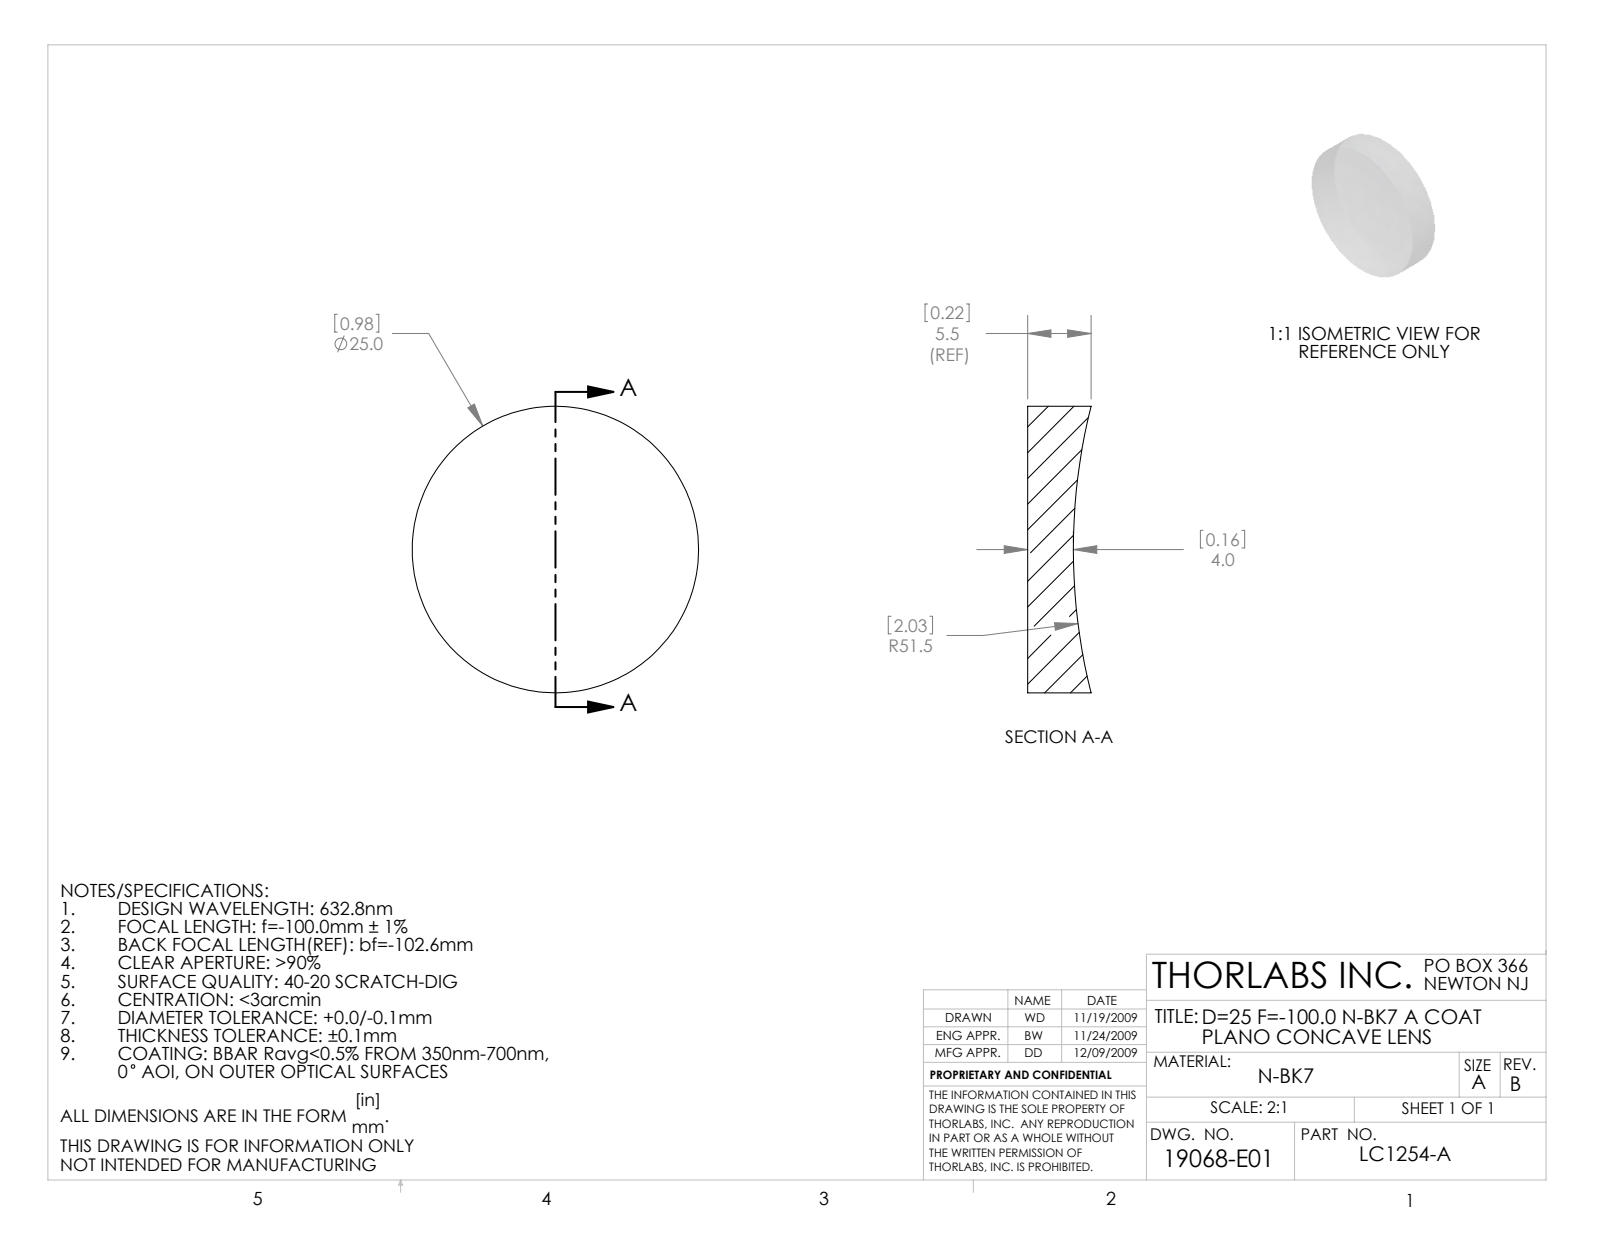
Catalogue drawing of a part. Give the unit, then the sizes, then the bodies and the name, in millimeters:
Units: millimetres
Overall size (bounding box): 25 × 25 × 5.54
Round bosses / shafts (diameter × count): ⌀25 ×1
Volume: 2 340 mm³ · Surface area: 1 424 mm²
Bodies: 1 solid, 5 faces (1 planar, 2 cylindrical, 2 other)
Part name (STEP PRODUCT): 19068-E0W
STEP written by: SolidWorks 2009 (AUTOMOTIVE_DESIGN)
